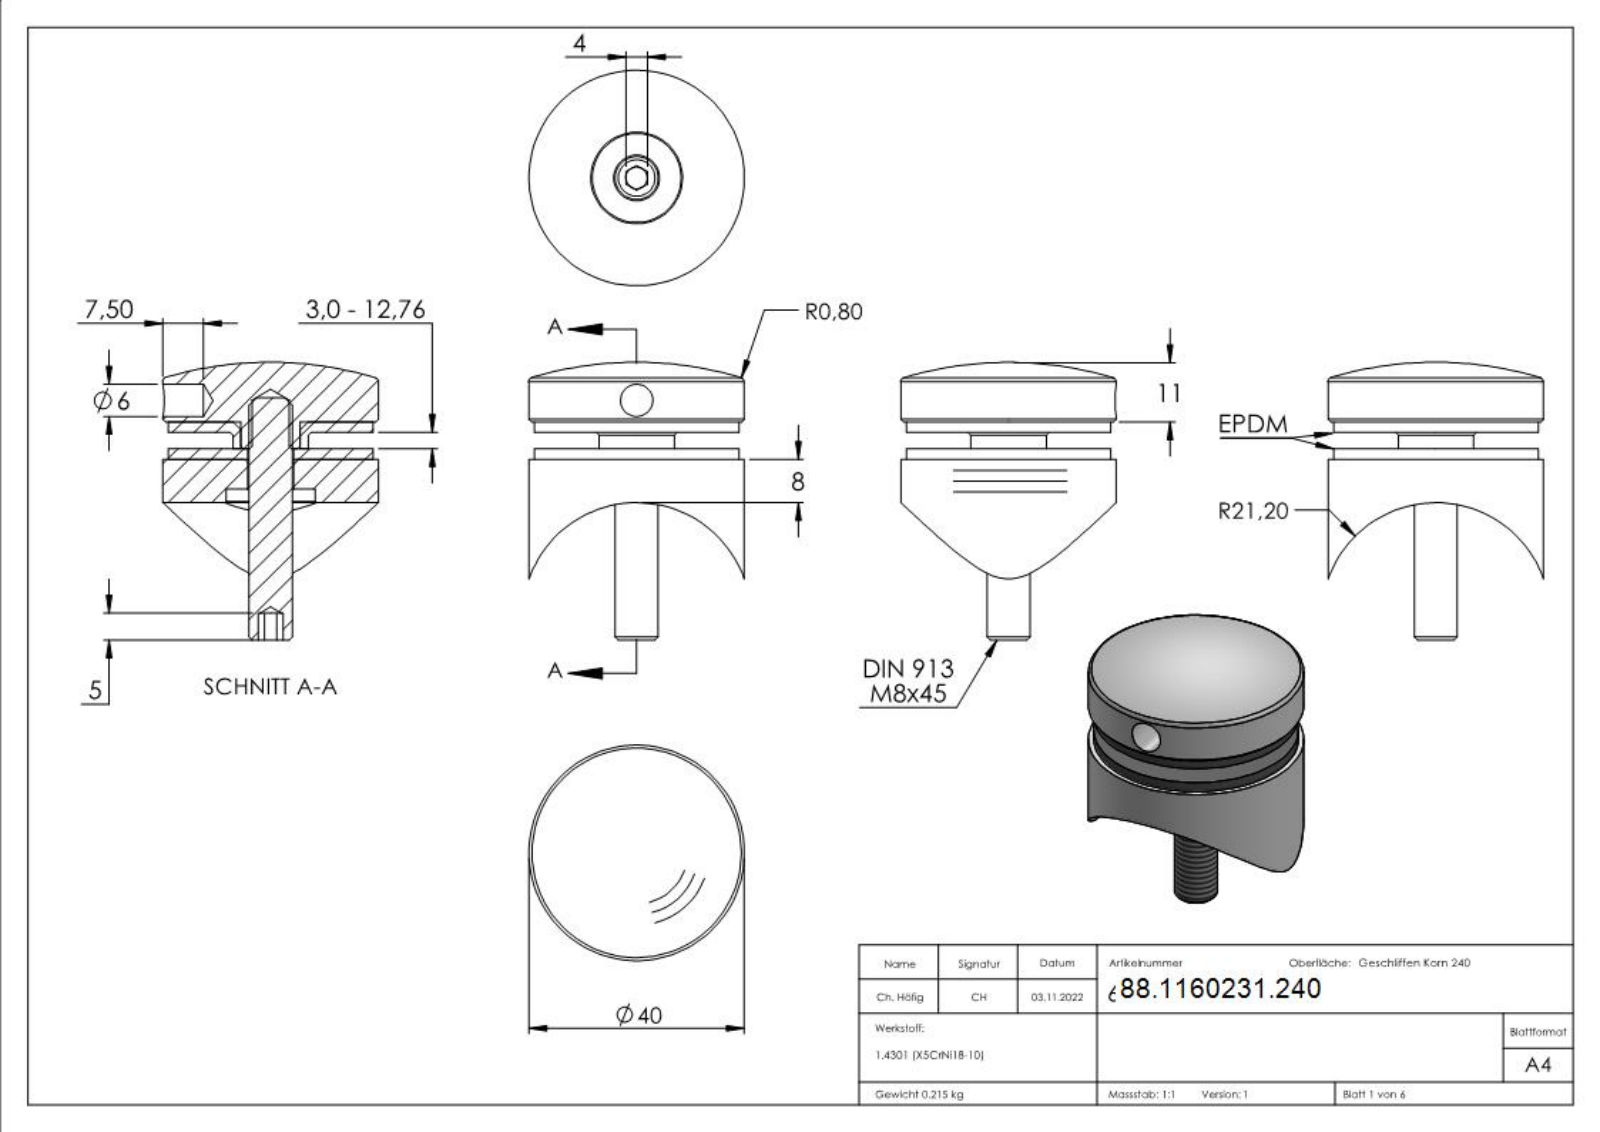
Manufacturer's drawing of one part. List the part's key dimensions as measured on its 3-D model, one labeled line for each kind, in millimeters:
Part name (STEP PRODUCT): 6023X-240 Teil4_6023X-240 Teil4; DIN913_DIN 913 M8x45; 60231-240; 60230-240 Teil2_60231-240 Teil 2 (+2 more)
STEP written by: SolidWorks 2018 (CONFIG_CONTROL_DESIGN)
Units: millimetres
Bodies: 5 solids, 277 faces (137 planar, 16 cylindrical, 124 other)
Overall size (bounding box): 51.52 × 40 × 40
Volume: 30 912 mm³ · Surface area: 15 020 mm²
Round holes (diameter × count): ⌀6 ×1, ⌀6.8 ×1, ⌀8.5 ×1, ⌀11 ×1, ⌀16.5 ×1, ⌀17 ×1
Round bosses / shafts (diameter × count): ⌀40 ×1, ⌀38 ×1, ⌀14 ×1, ⌀8 ×1
Partial cylindrical surfaces — rounded edges, fillets, slot ends (radius × count): R21.2 ×1
Main face-to-face distances: 5, 2, 7, 3, 5.5, 7.5, 10.5, 12.5, 4, 33.52
